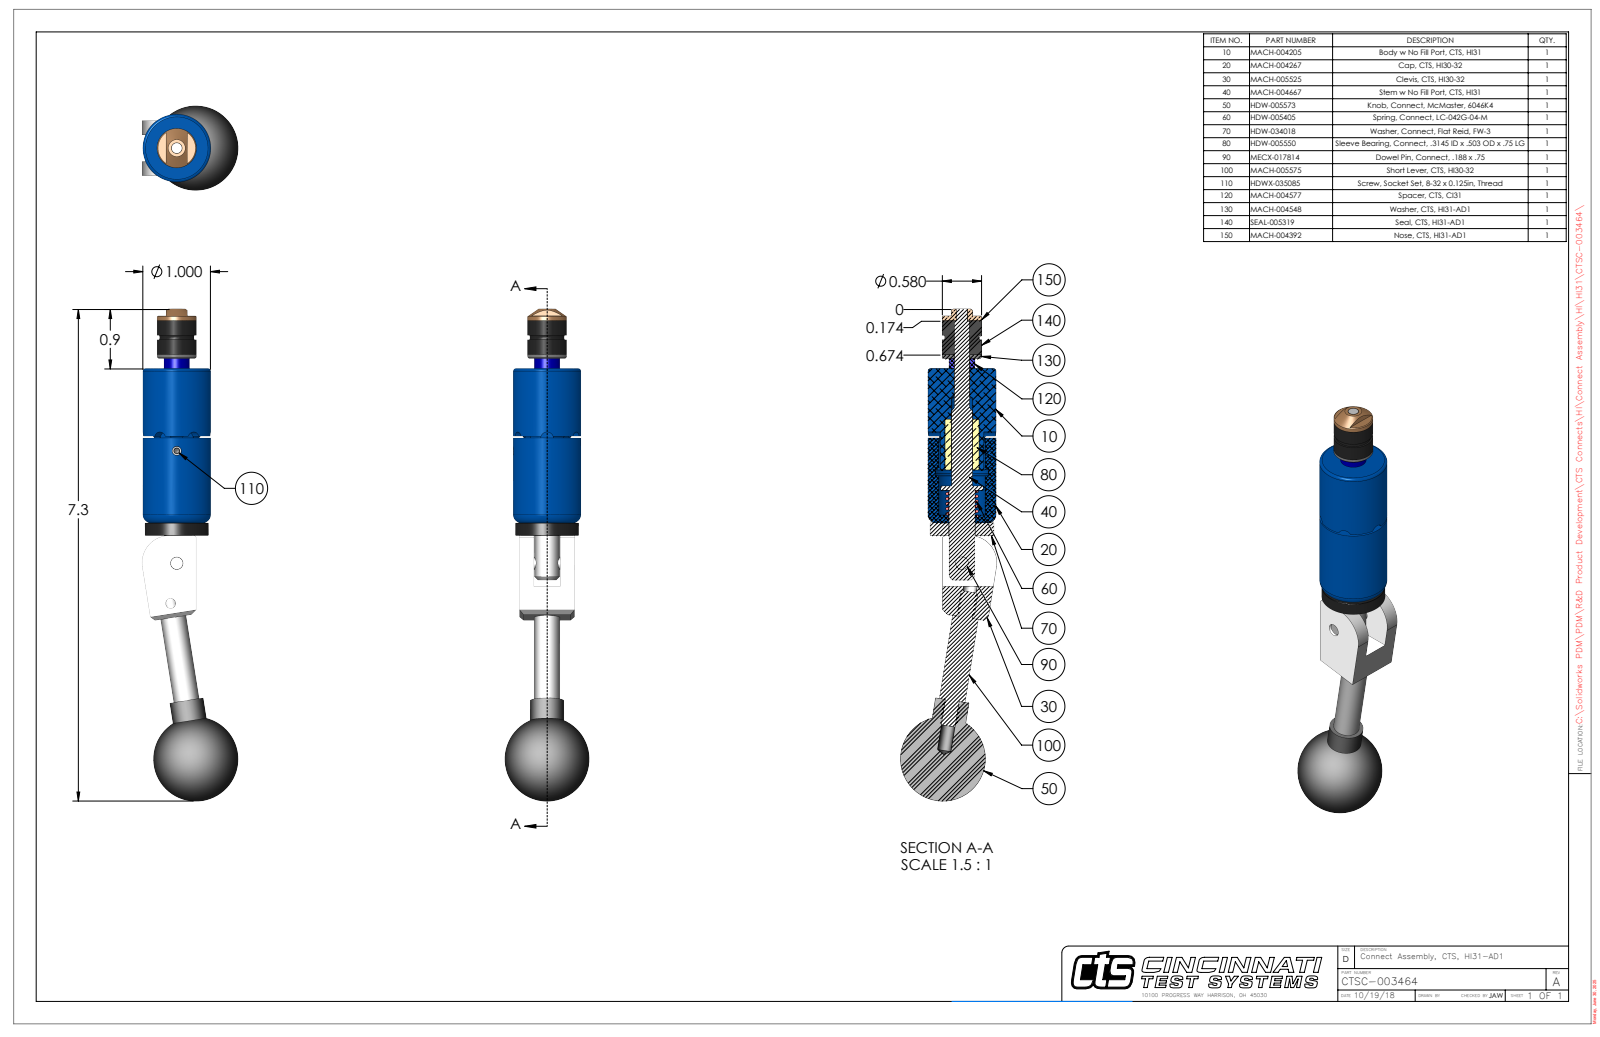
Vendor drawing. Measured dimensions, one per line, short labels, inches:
name: CTSC-003464
written by: SolidWorks 2023 (AUTOMOTIVE_DESIGN)
unit: in
bodies: 10 solids, 254 faces (98 planar, 99 cylindrical, 57 other)
size: 7.268 × 1.416 × 1.25
volume: 3.843 in³; area: 31.69 in²
holes: 2× ⌀0.201, 1× ⌀0.136, 1× ⌀0.15, 1× ⌀0.159, 1× ⌀0.189, 1× ⌀0.218, 1× ⌀0.228, 1× ⌀0.229, 1× ⌀0.385, 1× ⌀0.392
bosses: 1× ⌀1, 1× ⌀0.936, 1× ⌀0.58, 1× ⌀0.5, 1× ⌀0.38, 1× ⌀0.379, 1× ⌀0.375, 1× ⌀0.25
rounds: 6× R0.093, 2× R0.029, 1× R0.344, 1× R0.4, 1× R0.468
face distances: 0.21, 0.602, 0.812, 0.187, 2.28, 2.467, 0.391, 0.705, 2.985, 3.172
hole spacings: 0.599, 1.658, 2.252
